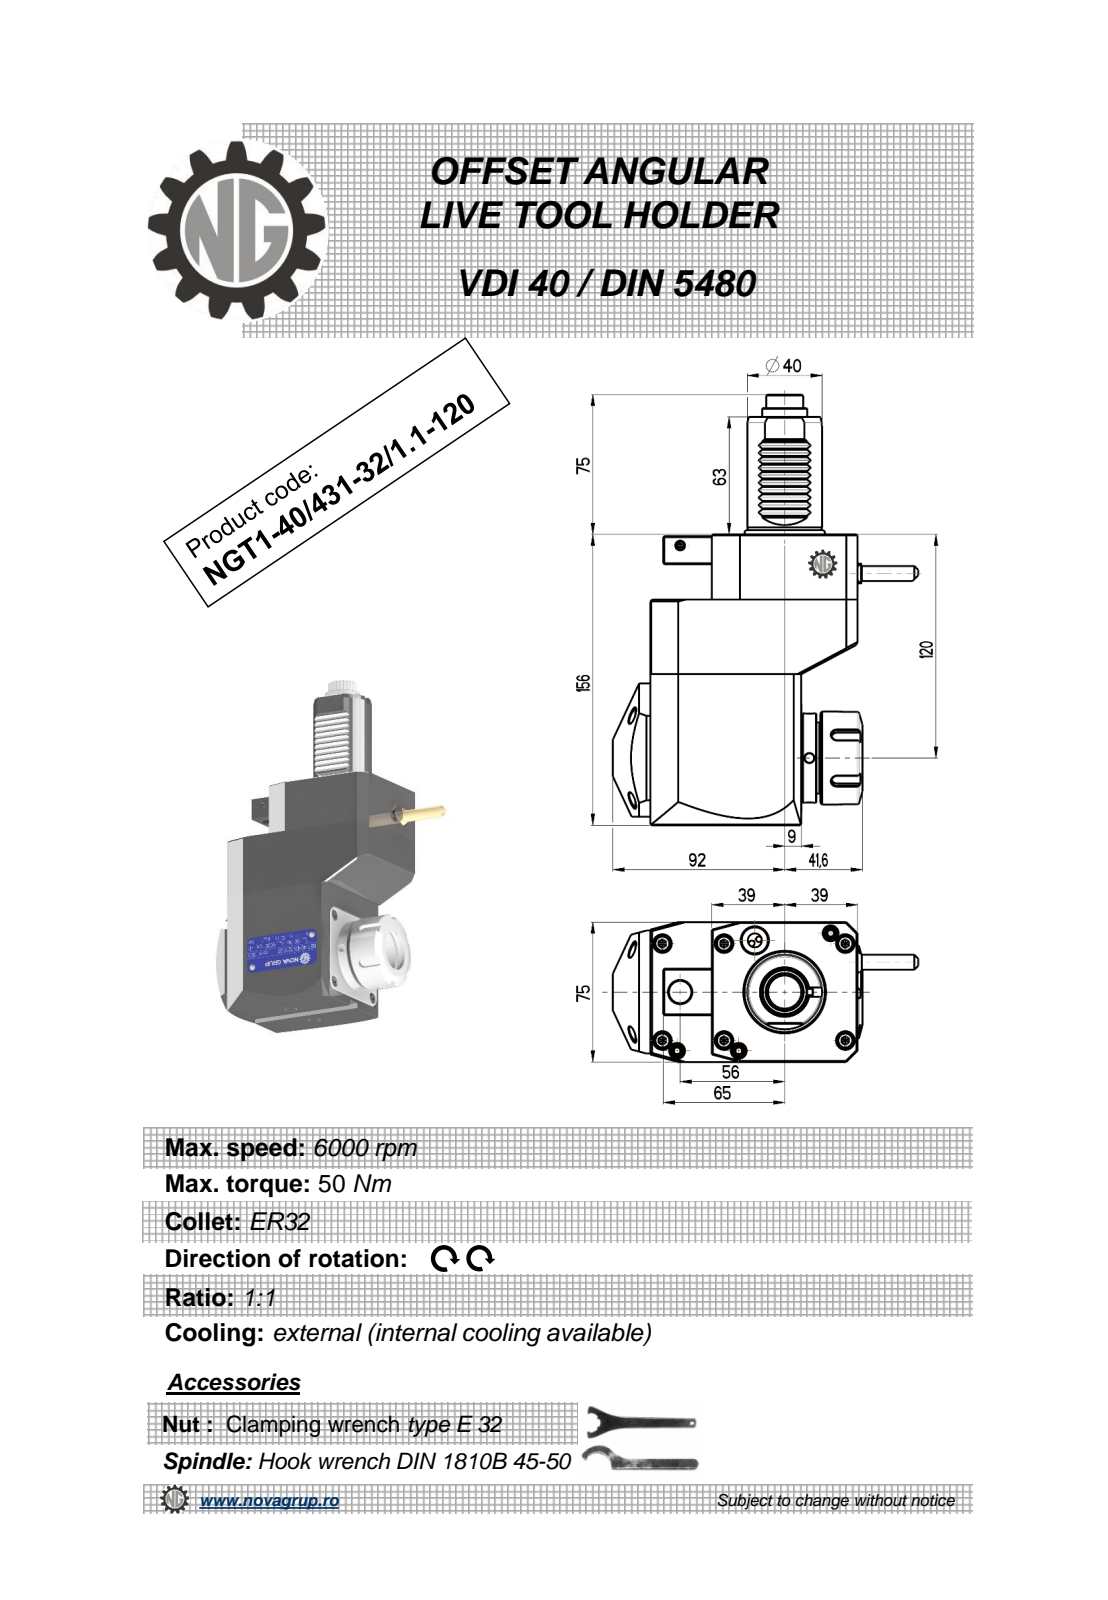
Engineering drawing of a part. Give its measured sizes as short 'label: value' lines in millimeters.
name: NGT1_40_431_32_1_1_120
written by: PRO/ENGINEER BY PARAMETRIC TECHNOLOGY CORPORATION, 2010280 (CONFIG_CONTROL_DESIGN)
unit: mm
bodies: 1 solid, 528 faces (197 planar, 181 cylindrical, 150 other)
size: 231 × 163.5 × 76.6
volume: 1 192 000 mm³; area: 87 557 mm²
holes: 3× ⌀5, 1× ⌀3, 1× ⌀4.2, 1× ⌀9.5, 1× ⌀12, 1× ⌀27
bosses: 1× ⌀50, 1× ⌀48, 1× ⌀41, 1× ⌀40, 1× ⌀24, 1× ⌀11.2, 1× ⌀8.96, 1× ⌀8
rounds: 48× R2.08, 12× R0.26, 10× R0.3, 6× R0.22, 5× R3, 1× R9.08, 1× R9.92, 1× R15
face distances: 75, 156, 111, 35, 121, 30, 81, 33, 48, 78
hole spacings: 20.3, 69.25, 100.28, 111.5, 133.39
